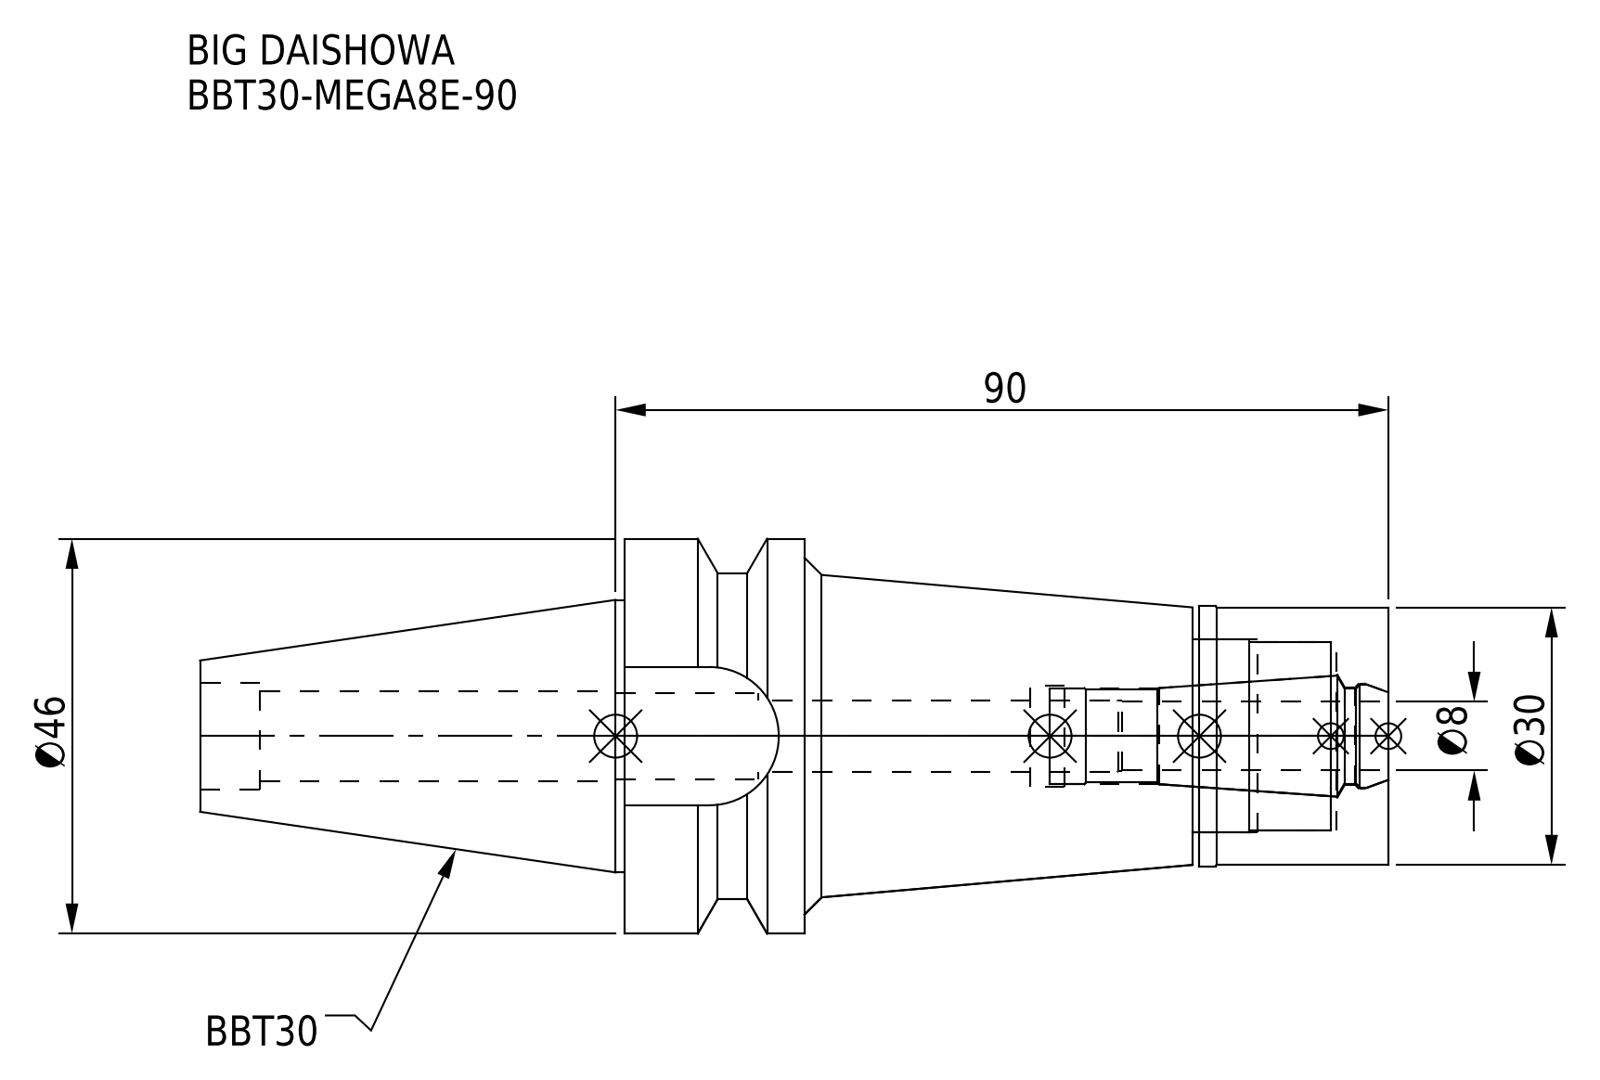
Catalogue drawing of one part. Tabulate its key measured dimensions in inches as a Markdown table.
| quantity | value |
| --- | --- |
| part name | BBT30ME08090-080_ASM.stp; BBT30-MEGA8E-90-080.stp; MEN8_1.stp; BBT30-MEGA8E-90 (+3 more) |
| STEP written by | SolidWorks 2019 (CONFIG_CONTROL_DESIGN) |
| units | inches |
| bodies | 2 solids, 79 faces (21 planar, 38 cylindrical, 20 other) |
| overall size | 5.449 × 1.811 × 1.811 |
| volume | 6.021 in³ |
| surface area | 37.94 in² |
| round holes (diameter × count) | 0.331 × 1, 0.394 × 1, 0.409 × 1, 0.441 × 1, 0.449 × 1, 0.465 × 1, 0.484 × 1, 0.492 × 1, 0.866 × 1, 0.886 × 1 |
| round bosses / shafts (diameter × count) | 1.811 × 1, 1.25 × 1, 1.193 × 1, 1.181 × 1 |
| partial cylindrical surfaces (radius × count) | 0.317 × 1, 0.748 × 1 |
| main face-to-face distances | 3.504, 0.866, 0.634, 2.638, 2.677, 0.898, 0.031, 2.606, 1.811, 1.78 |
